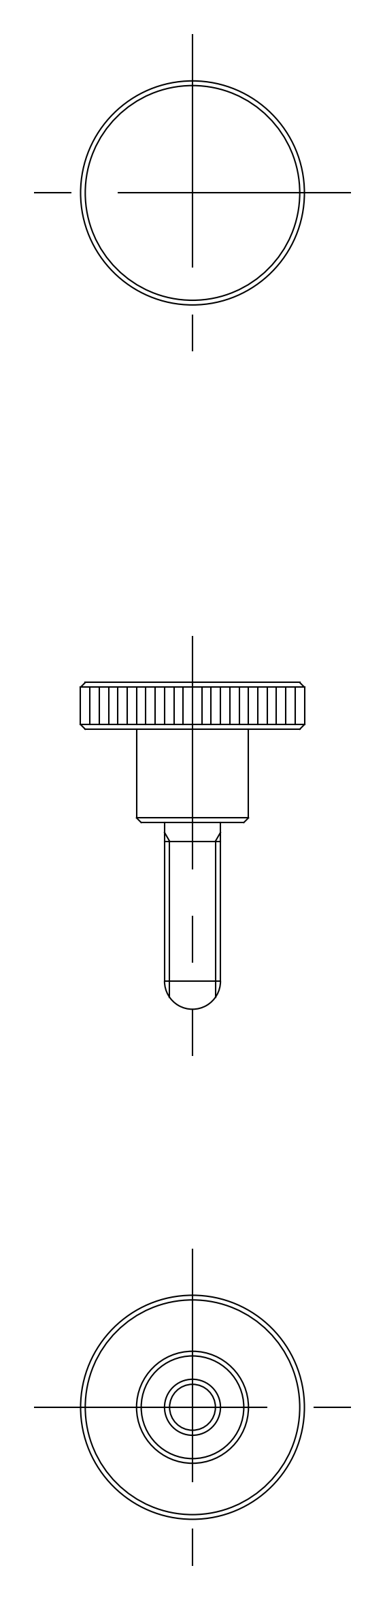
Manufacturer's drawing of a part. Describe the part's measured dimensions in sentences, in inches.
The part is named "knob". Its 3-D file was written by "CADfix (AUTOMOTIVE_DESIGN)". It is 1 solid with 16 faces: 0 planar, 0 cylindrical and 16 other. Overall it measures 1.378 by 0.945 by 0.945 inches. Its volume is 0.239 cubic inches and its surface area 3.026 square inches.
